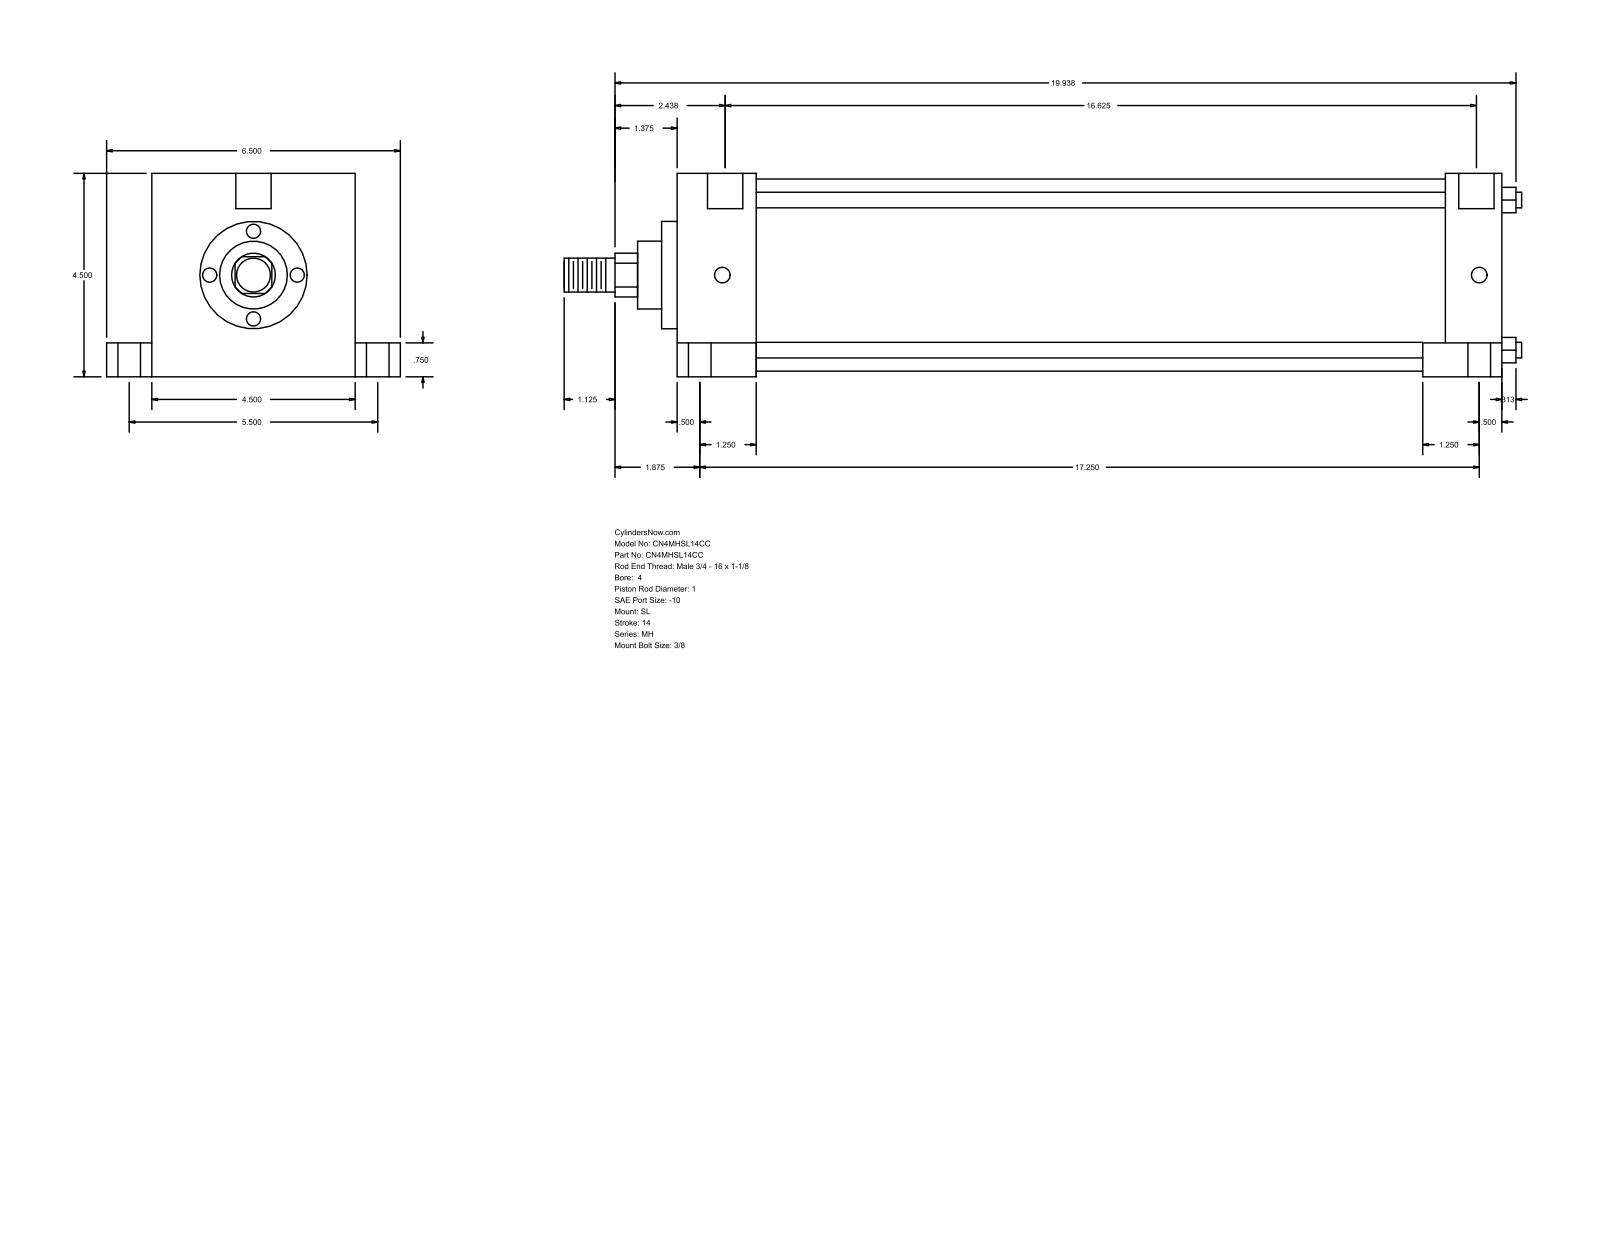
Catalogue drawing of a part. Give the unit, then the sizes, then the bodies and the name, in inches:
Units: inches
Overall size (bounding box): 21.187 × 6.5 × 4.5
Round holes (diameter × count): ⌀0.344 ×4, ⌀0.5 ×4, ⌀0.75 ×4, ⌀0.781 ×2
Round bosses / shafts (diameter × count): ⌀0.345 ×4, ⌀4.25 ×1, ⌀2.375 ×1, ⌀1.5 ×1, ⌀1 ×1, ⌀0.75 ×1
Partial cylindrical surfaces — rounded edges, fillets, slot ends (radius × count): R0.484 ×1
Main face-to-face distances: 4.5, 18.25, 1.75, 16.5, 17, 15.25, 1.25, 1, 5.5, 0.75
Hole centre spacings: 0.062, 2.75, 2.751, 2.795, 2.807, 5.5, 16.687, 16.75
Bodies: 0 solids, 110 faces (77 planar, 33 cylindrical, 0 other)
Part name (STEP PRODUCT): MH_SL__0400_1
STEP written by: GSSL Pune (CONFIG_CONTROL_DESIGN)
